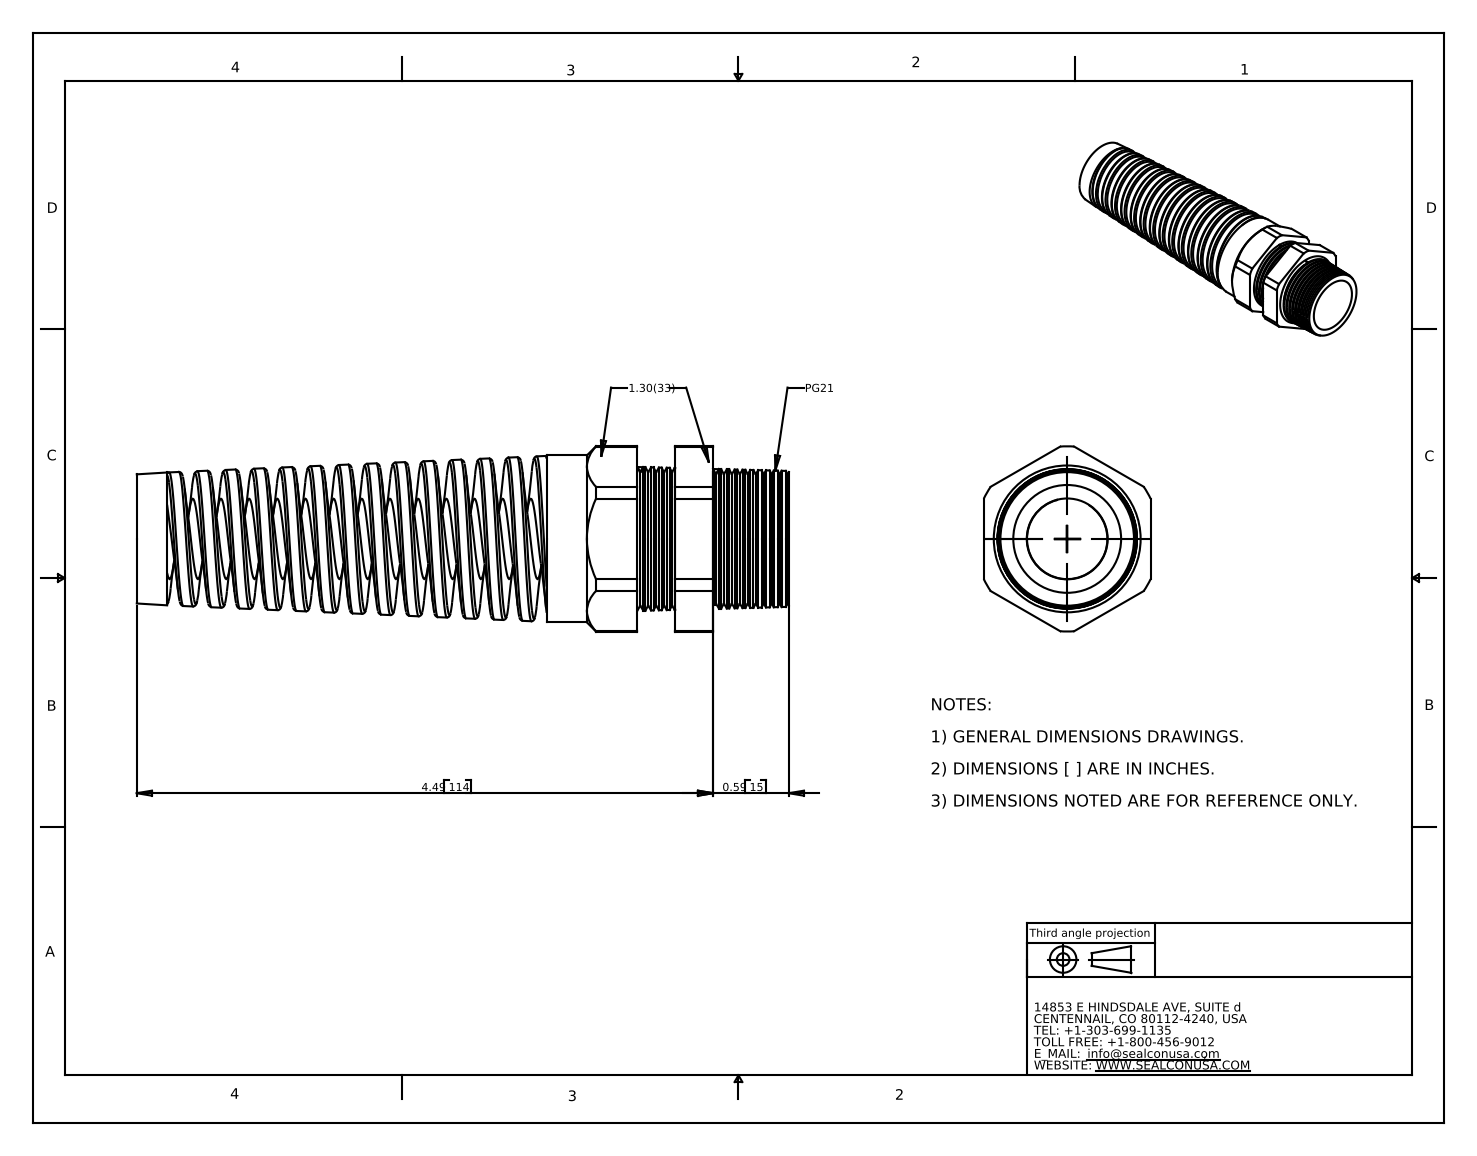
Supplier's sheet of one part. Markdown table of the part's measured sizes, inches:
| quantity | value |
| --- | --- |
| part name | CF21CR-BK |
| STEP written by | SolidWorks 2007 (CONFIG_CONTROL_DESIGN) |
| units | inches |
| bodies | 2 solids, 216 faces (24 planar, 53 cylindrical, 139 other) |
| overall size | 5.08 × 1.443 × 1.3 |
| volume | 2.956 in³ |
| surface area | 48.5 in² |
| round holes (diameter × count) | 0.626 × 1, 0.63 × 1, 0.655 × 1 |
| round bosses / shafts (diameter × count) | 1.3 × 1, 0.84 × 1 |
| partial cylindrical surfaces (radius × count) | 0.721 × 1 |
| main face-to-face distances | 1.3, 0.295, 3.9, 4.195, 4.491, 0.59, 0.295, 3.193, 0.707, 1.002 |
